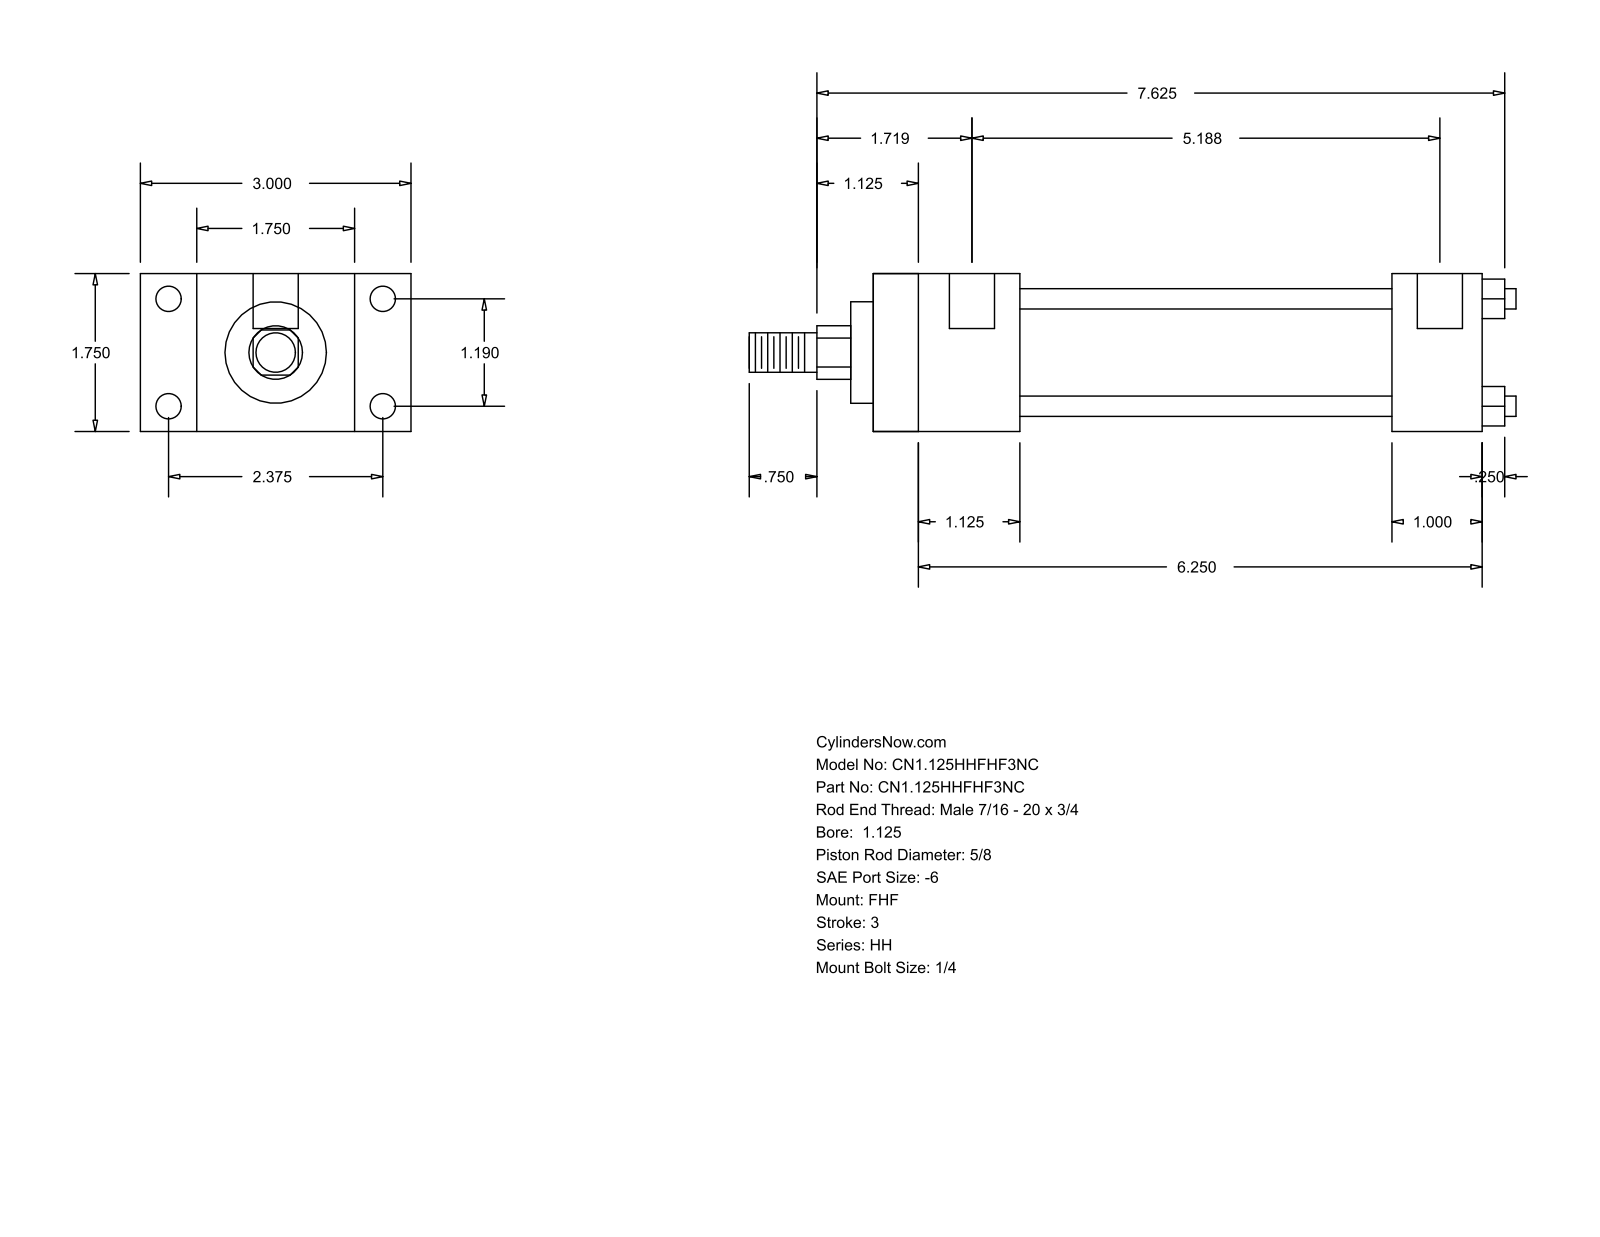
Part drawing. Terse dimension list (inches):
name: HH_FHF__0112_0.625
written by: GSSL Pune (CONFIG_CONTROL_DESIGN)
unit: in
bodies: 0 solids, 88 faces (60 planar, 28 cylindrical, 0 other)
size: 8.5 × 3 × 1.75
holes: 4× ⌀0.219, 4× ⌀0.281, 2× ⌀0.5
bosses: 4× ⌀0.225, 1× ⌀1.375, 1× ⌀1.125, 1× ⌀0.625, 1× ⌀0.437
rounds: 1× R0.297
face distances: 1.75, 0.625, 2.375, 1.625, 3, 6.75, 5.125, 5.75, 4.125, 1
hole spacings: 1.19, 2.375, 2.656, 5.063, 0.125, 5.187
